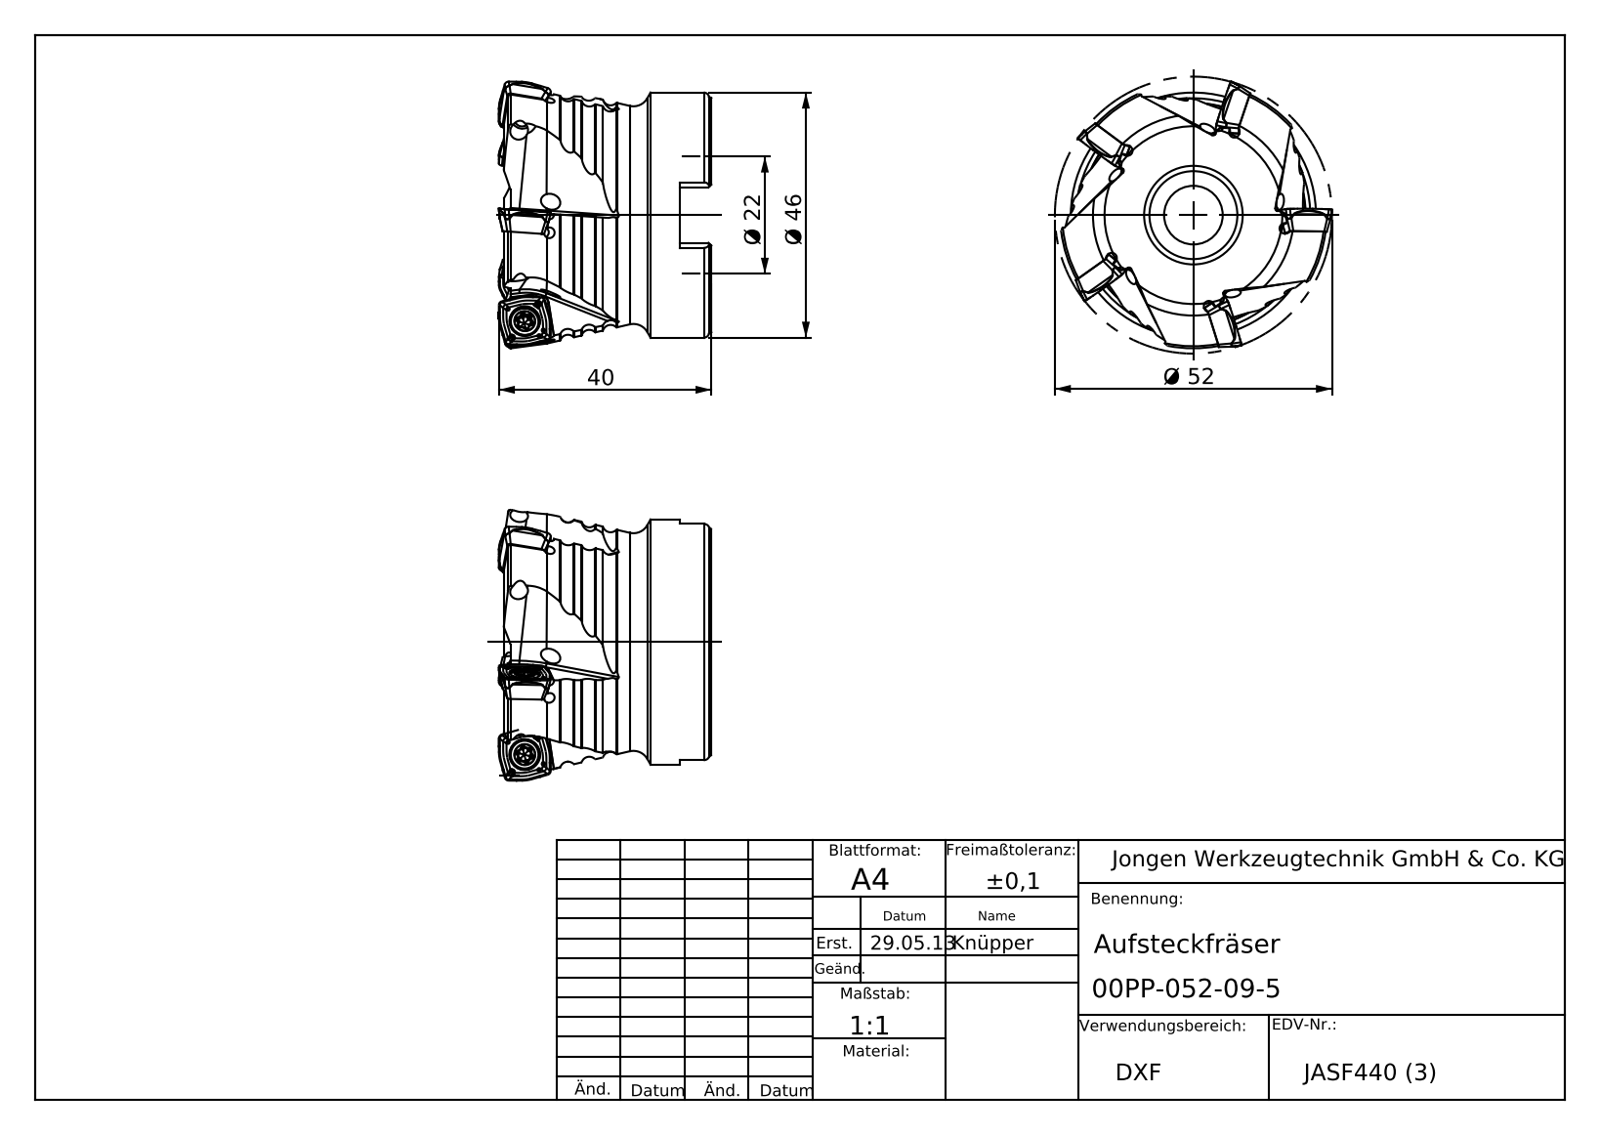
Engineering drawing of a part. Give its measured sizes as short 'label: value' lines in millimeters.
name: 00PP-052-09-5
written by: SolidWorks 2013 (AUTOMOTIVE_DESIGN)
unit: mm
bodies: 1 solid, 215 faces (68 planar, 46 cylindrical, 101 other)
size: 51.98 × 51.98 × 40.05
volume: 50 669 mm³; area: 13 581 mm²
holes: 5× ⌀3, 1× ⌀11, 1× ⌀16.5, 1× ⌀21.85, 1× ⌀22.15, 1× ⌀22.3
bosses: 1× ⌀46
rounds: 10× R0.5, 10× R0.8, 10× R1, 5× R2
face distances: 37.75, 5.93, 31.82, 10.4, 27, 21.07, 10.75, 20, 14.07, 7
